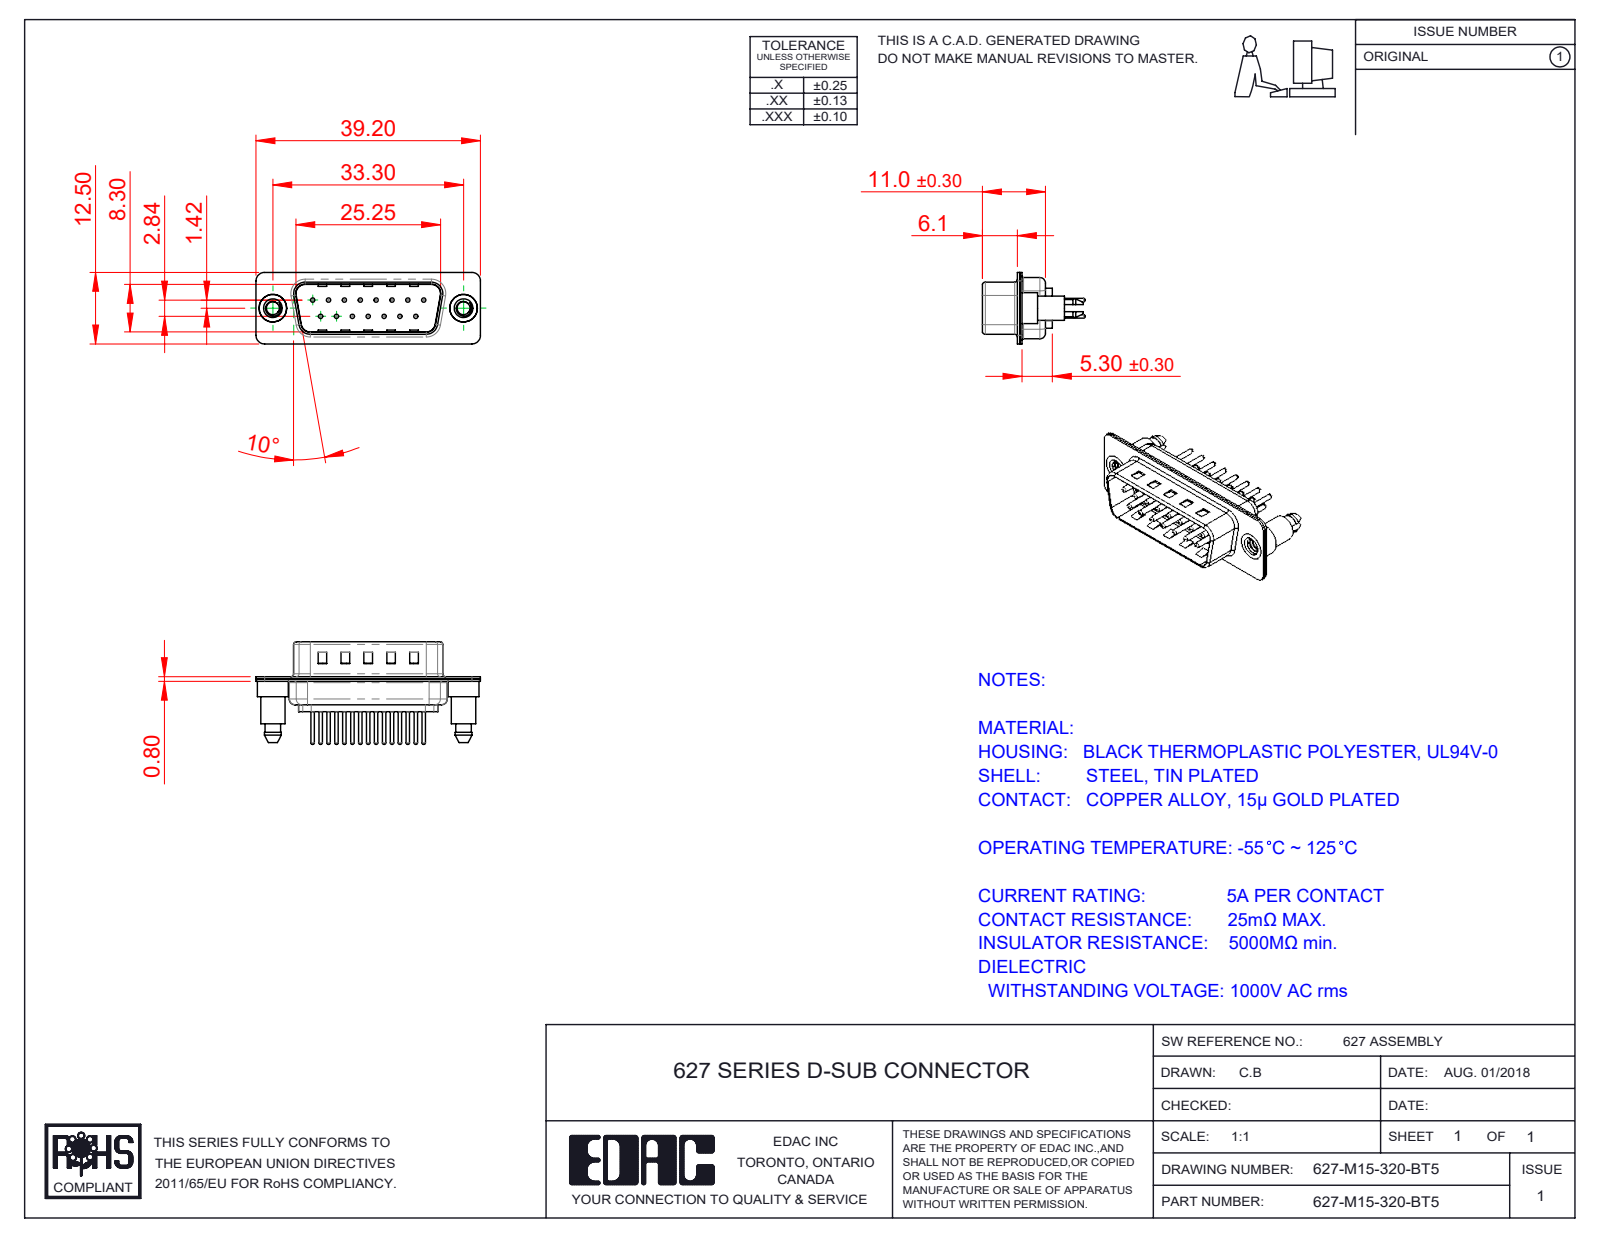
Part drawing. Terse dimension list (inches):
name: 627M Contact Row 1_20; 627M Shell Front_15 Contacts; 627M Contact Row 2_20; 627-M15-320-BT5 (+3 more)
written by: SolidWorks 2020 (CONFIG_CONTROL_DESIGN)
unit: in
bodies: 20 solids, 945 faces (260 planar, 375 cylindrical, 310 other)
size: 1.543 × 0.705 × 0.492
volume: 0.121 in³; area: 7.969 in²
holes: 15× ⌀0.03, 15× ⌀0.063, 15× ⌀0.079, 2× ⌀0.089, 2× ⌀0.157, 2× ⌀0.189
bosses: 15× ⌀0.059, 15× ⌀0.024, 2× ⌀0.213, 2× ⌀0.193, 2× ⌀0.167
rounds: 18× R0.059, 12× R0.079, 10× R0.063, 8× R0.02, 4× R0.01, 4× R0.024, 4× R0.026, 4× R0.035
face distances: 0.016, 0.031, 0.374, 0.358, 0.343, 0.39, 0.209, 0.047, 0.24, 0.224
hole spacings: 0.124, 0.109, 0.218, 0.327, 0.436, 0.198, 0.198, 0.294
